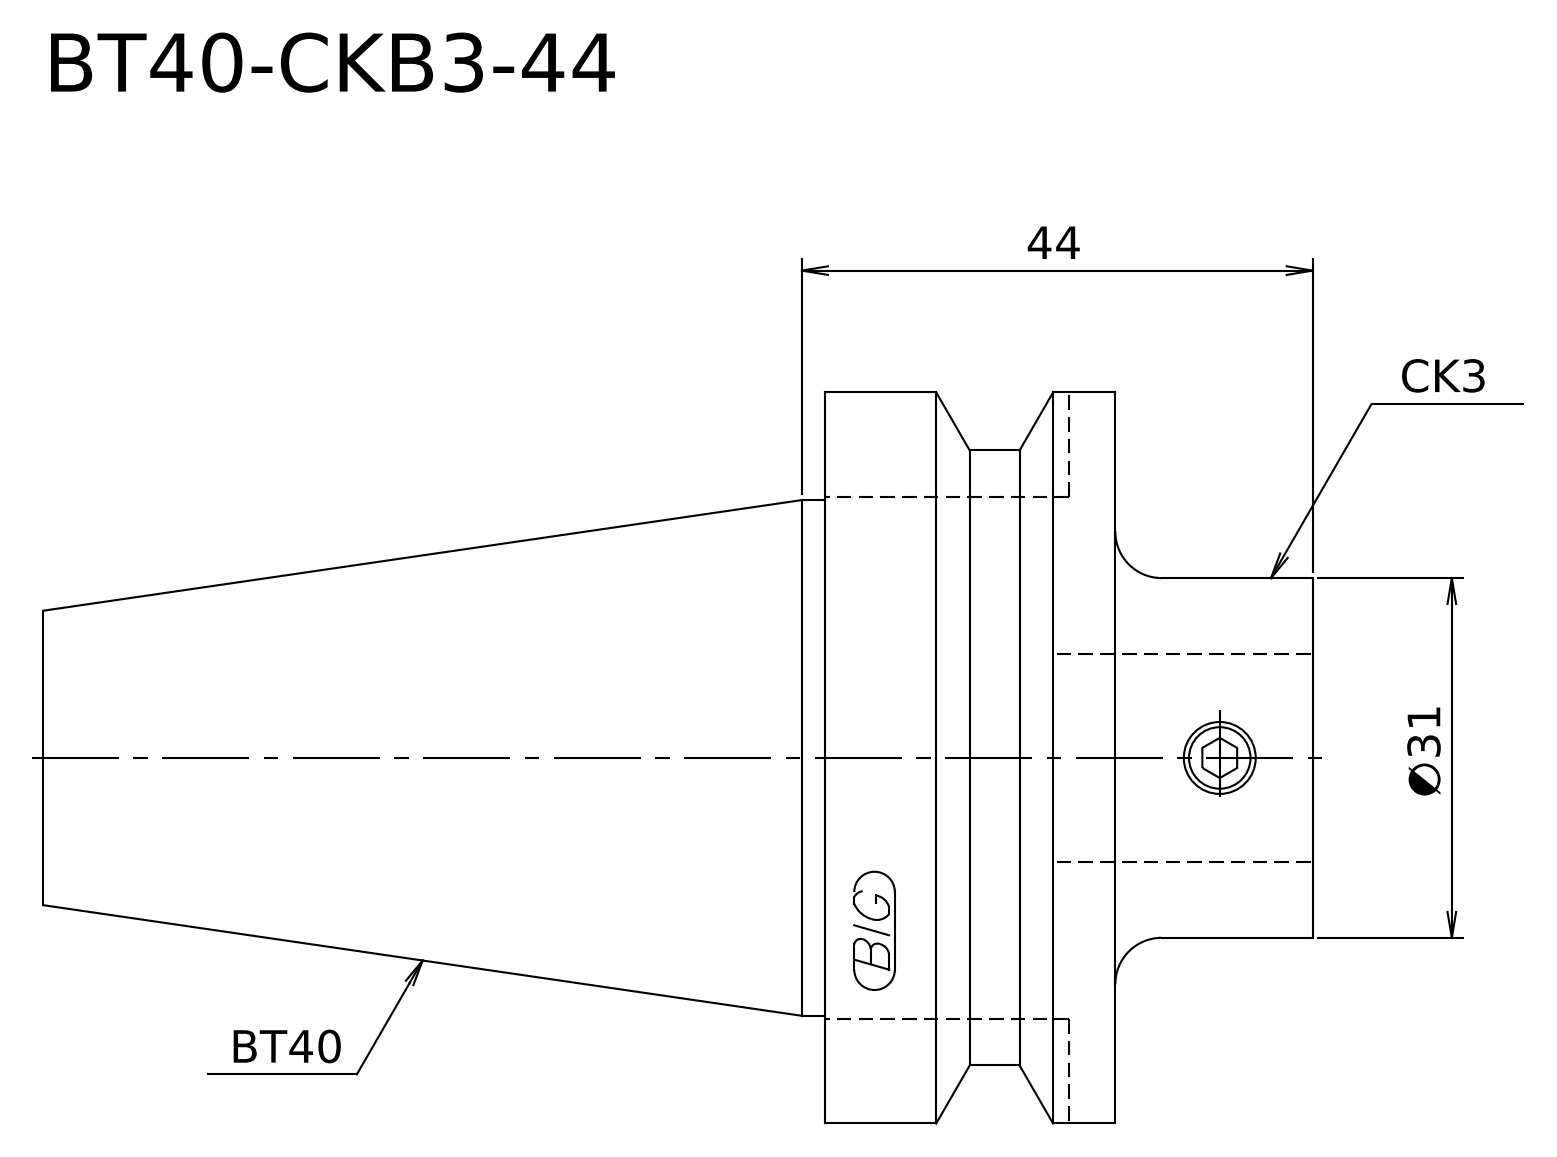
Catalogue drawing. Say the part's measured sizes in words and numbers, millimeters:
Its 3-D file was written by "Kubotek KeyCreator V8.5.1 (14335) (CONFIG_CONTROL_DESIGN)". It is 1 solid with 14 faces: 4 planar, 5 cylindrical and 5 other. Overall it measures 109.4 by 63 by 63 millimeters. Its volume is 152 796 cubic millimeters and its surface area 19 853 square millimeters. Round bosses or shafts: 1 of diameter 63, 1 of diameter 53, 1 of diameter 44.45, 1 of diameter 31. The main face-to-face distances are 25, 17, 42, 109.4, 92.4, 67.4.
